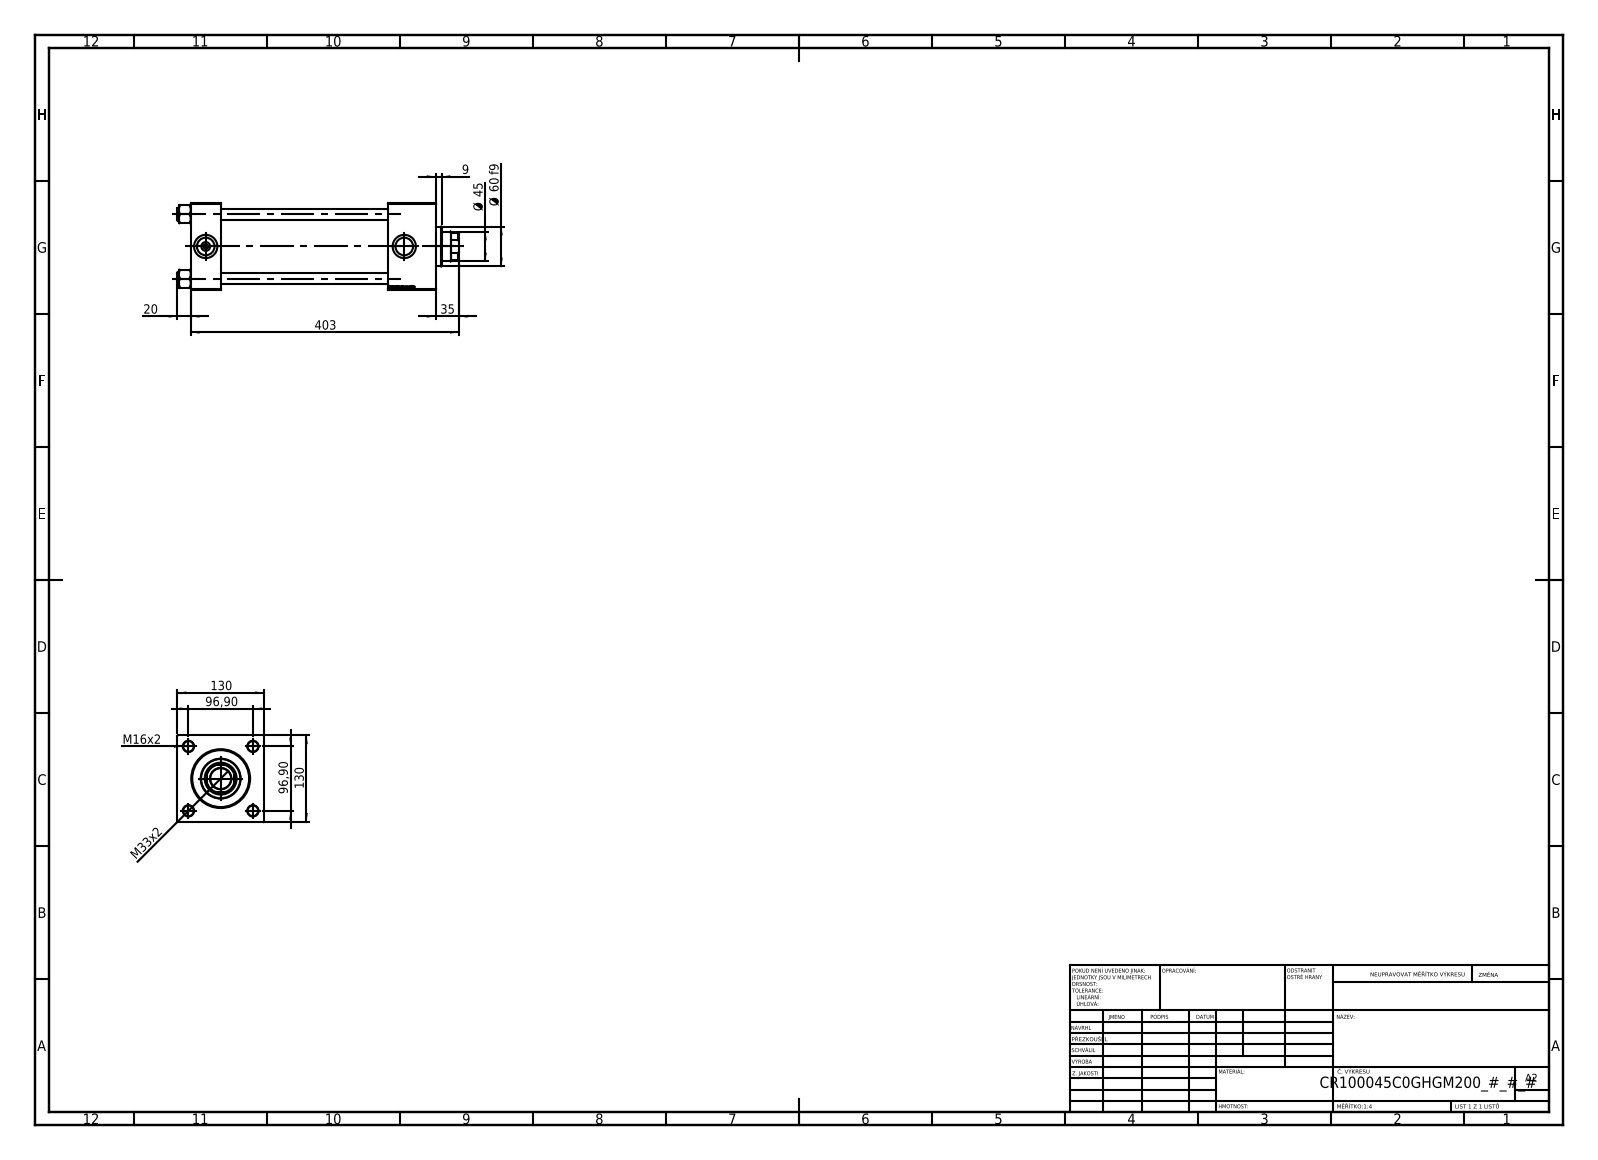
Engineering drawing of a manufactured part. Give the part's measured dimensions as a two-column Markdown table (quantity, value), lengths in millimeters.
| quantity | value |
| --- | --- |
| part name | V215CR_C_TYCINKA; V215CR_VCP_C; V215_VC_A; NUT_M5_C (+1 more) |
| STEP written by | SolidWorks 2019 (CONFIG_CONTROL_DESIGN) |
| units | millimeters |
| bodies | 11 solids, 1196 faces (574 planar, 86 cylindrical, 536 other) |
| overall size | 423 × 130 × 130 |
| volume | 3 031 000 mm³ |
| surface area | 504 516 mm² |
| round holes (diameter × count) | 16 × 4, 7 × 2, 26.44 × 2, 35 × 2, 31.5 × 1, 45 × 1, 48 × 1, 76 × 1, 85.5 × 1, 100 × 1 |
| round bosses / shafts (diameter × count) | 19 × 4, 106 × 1, 60 × 1 |
| partial cylindrical surfaces (radius × count) | 22 × 1 |
| main face-to-face distances | 130, 45, 368, 323, 296, 251, 72, 96, 51, 200 |
| hole center spacings | 68.52, 96.9, 137.04, 298.5 |
